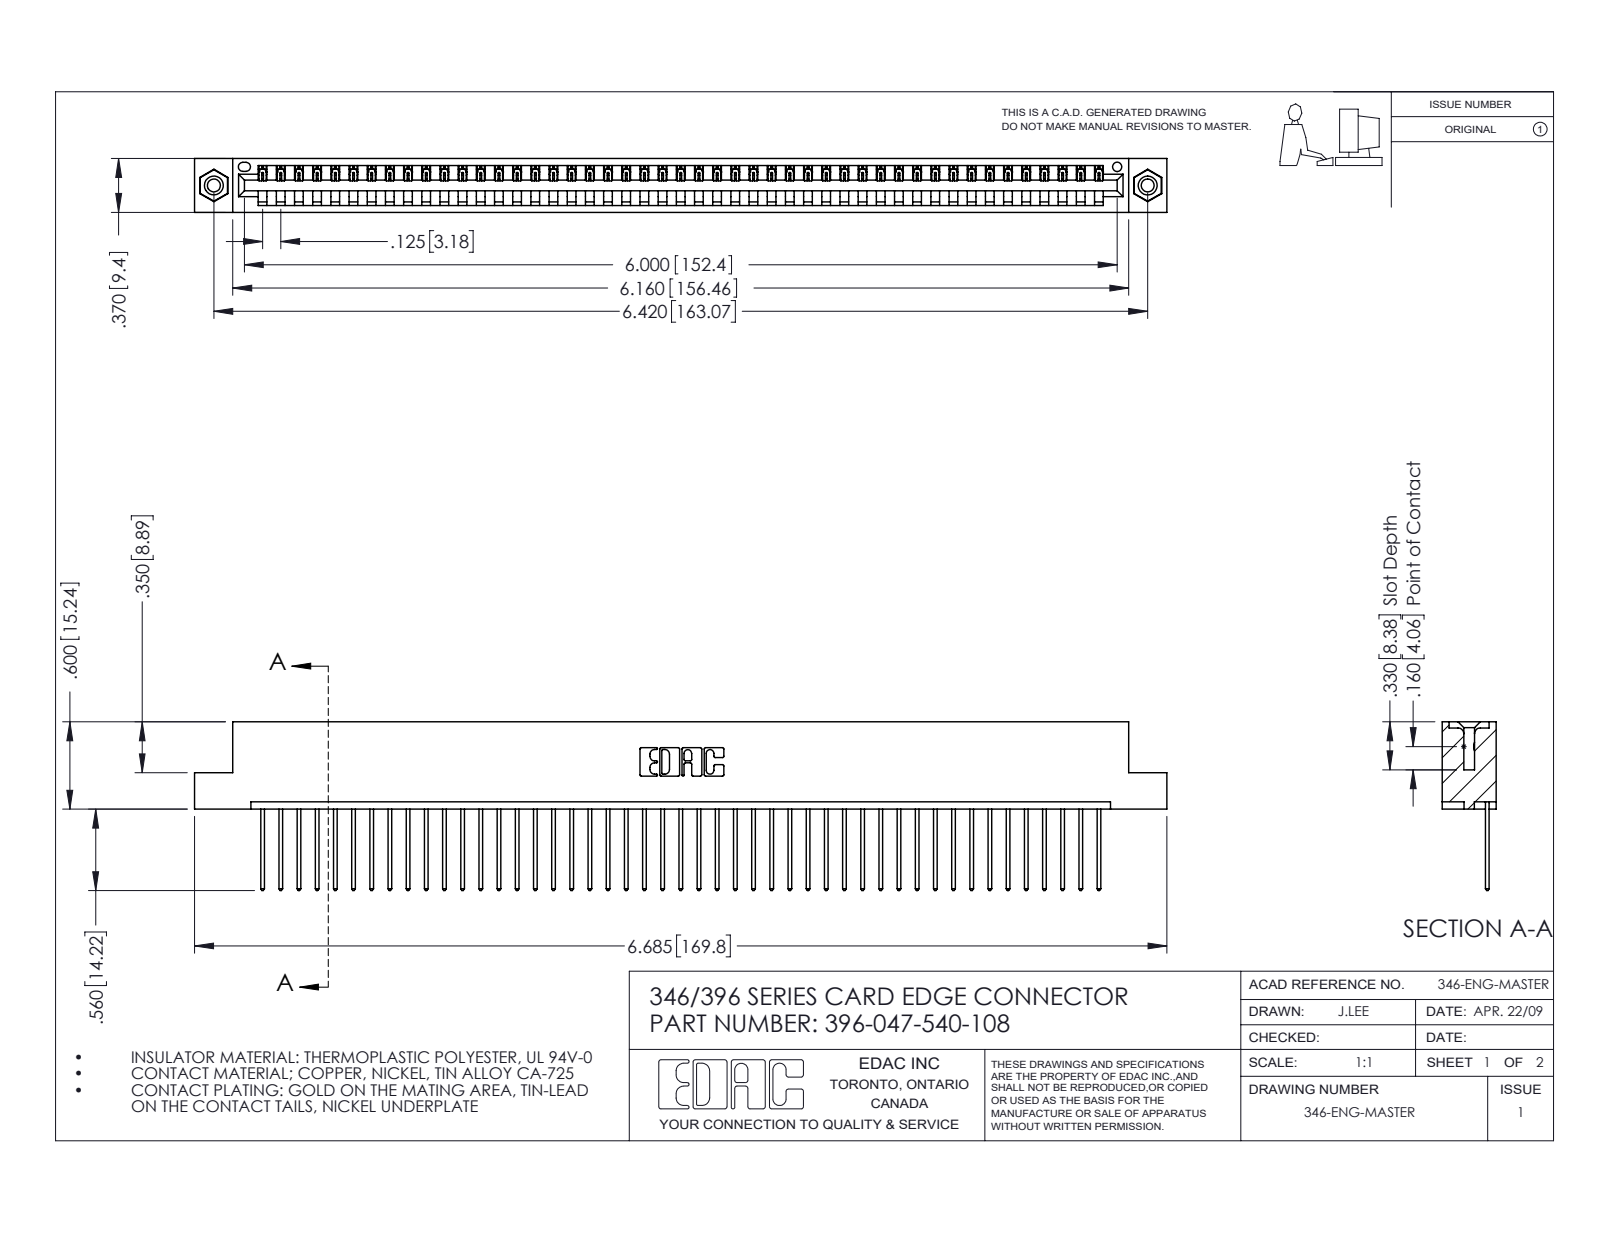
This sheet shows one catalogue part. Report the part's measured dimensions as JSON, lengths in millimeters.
{"part_name": "345-250-001_345-250-003-102; 396-047-540-108; 346 Part_Flush Mounting Lugs - 0.156 Dia-TI; 345-292-001_345-293-140", "step_written_by": "SolidWorks 2016 (CONFIG_CONTROL_DESIGN)", "units": "millimeters", "bodies": {"solids": 50, "faces": 2908, "planar": 1988, "cylindrical": 904, "other": 16}, "overall_size": [169.8, 29.5, 9.4], "volume_mm3": 16300, "surface_area_mm2": 20970, "round_holes": [[2.3, 2], [3.2, 2], [4, 2], [1.6, 1]], "round_bosses_or_shafts": [[3.9, 2]], "partial_cylinders_radius": [[0.2, 94], [0.3, 94], [0.3, 22], [0.2, 6], [0.8, 6], [0.7, 3], [0.8, 2], [1, 2]], "face_to_face_distances": [1.2, 8.2, 9.4, 6.4, 1.8, 7.6, 0.6, 3.8, 5.6, 2.5], "hole_center_spacings": [6.2, 157.8, 163.1]}
